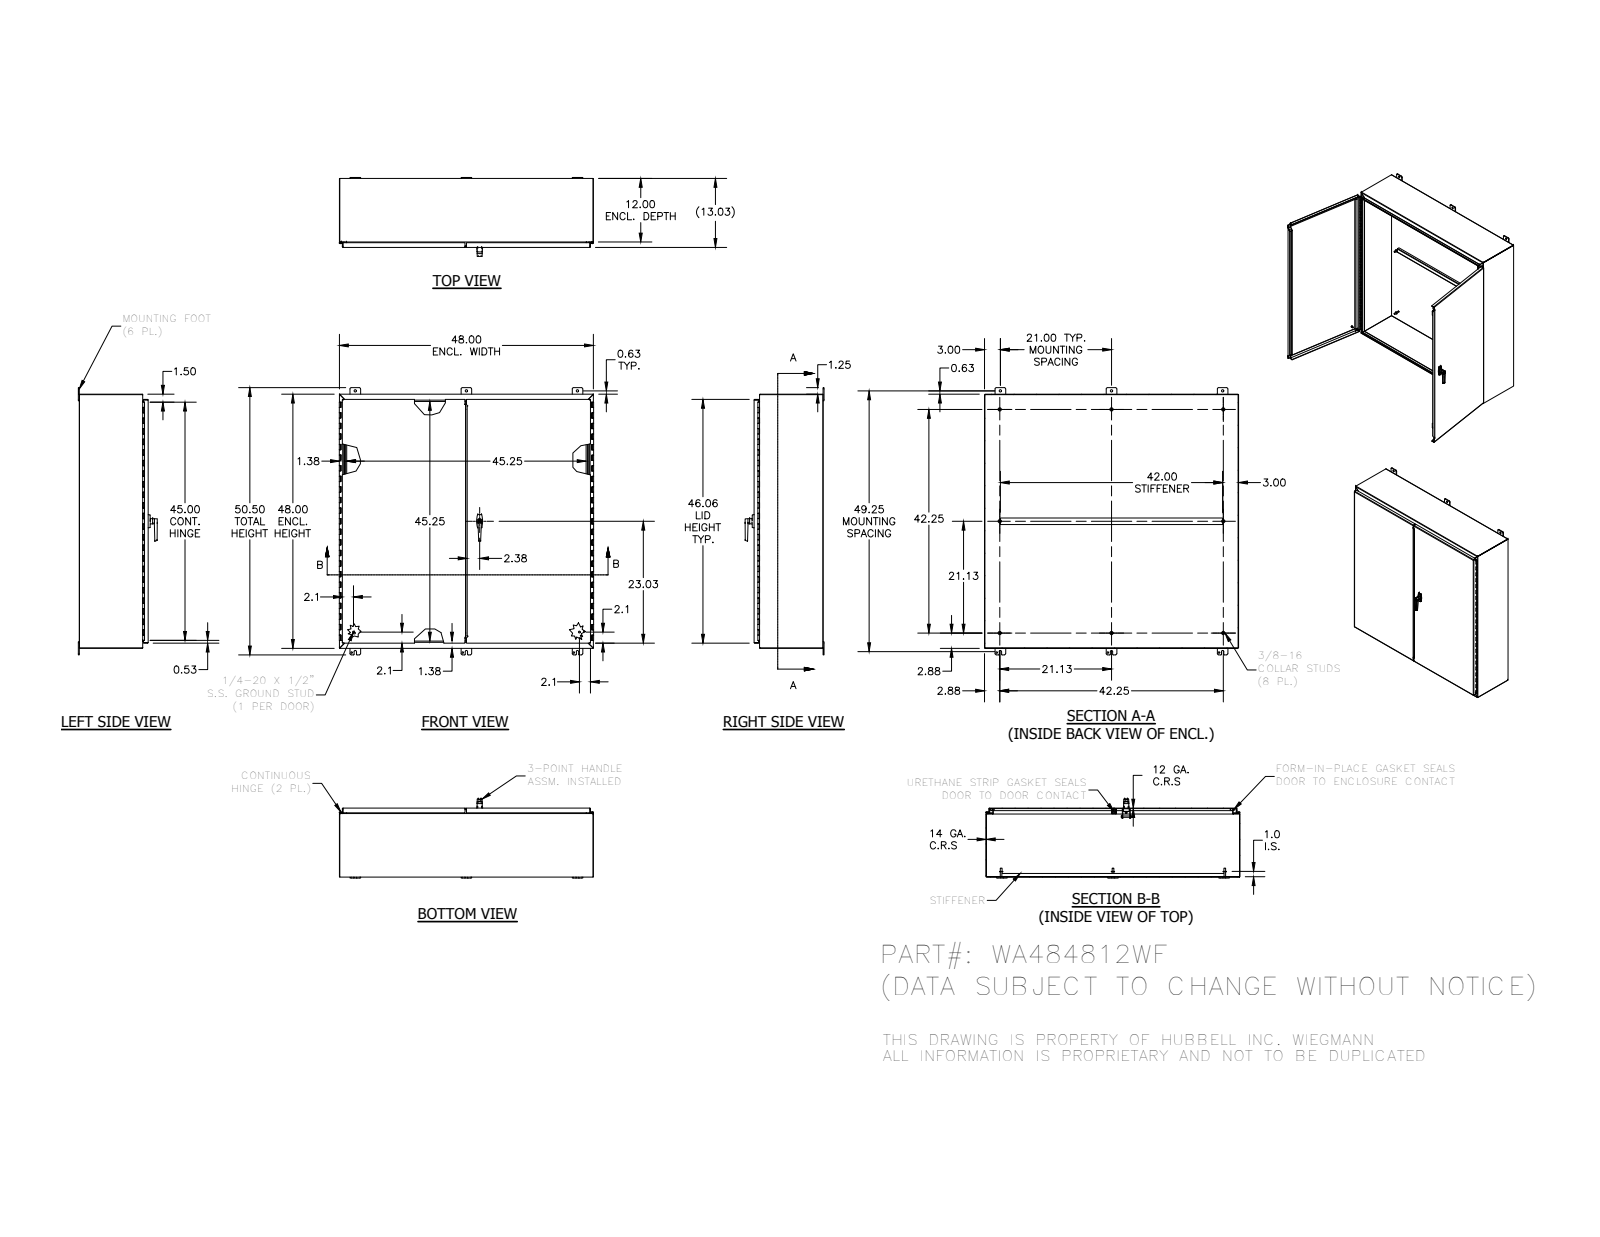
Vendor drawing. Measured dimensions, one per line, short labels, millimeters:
name: WA484812WFLRS; 34840; 38623; WA484812WFBTB (+8 more)
written by: Autodesk Inventor 2014 (AUTOMOTIVE_DESIGN)
unit: mm
bodies: 45 solids, 2677 faces (1517 planar, 711 cylindrical, 449 other)
size: 1282.7 × 1220.72 × 378.8
volume: 11 180 000 mm³; area: 10 450 000 mm²
holes: 8× ⌀7.02, 6× ⌀2.1, 6× ⌀7.95, 6× ⌀11.13, 4× ⌀5.08, 2× ⌀3.17, 2× ⌀4.04, 2× ⌀10.33, 1× ⌀1.5, 1× ⌀2.5, 1× ⌀3.3, 1× ⌀11.11
bosses: 8× ⌀15.88, 8× ⌀8.38, 7× ⌀4, 4× ⌀6.35, 2× ⌀13.37, 2× ⌀8.56, 2× ⌀6.34, 2× ⌀5.69
rounds: 30× R0.79, 24× R6.35, 22× R0.2, 22× R0.4, 19× R2.67, 16× R0.25, 12× R3.17, 8× R1
face distances: 1.88, 2.38, 1217.32, 328.58, 326.7, 330.96, 329.08, 1215.44, 1219.2, 302.92
hole spacings: 533.4, 1330.78, 7.45, 40.46, 1219.2, 5.1, 517.24, 552.06
